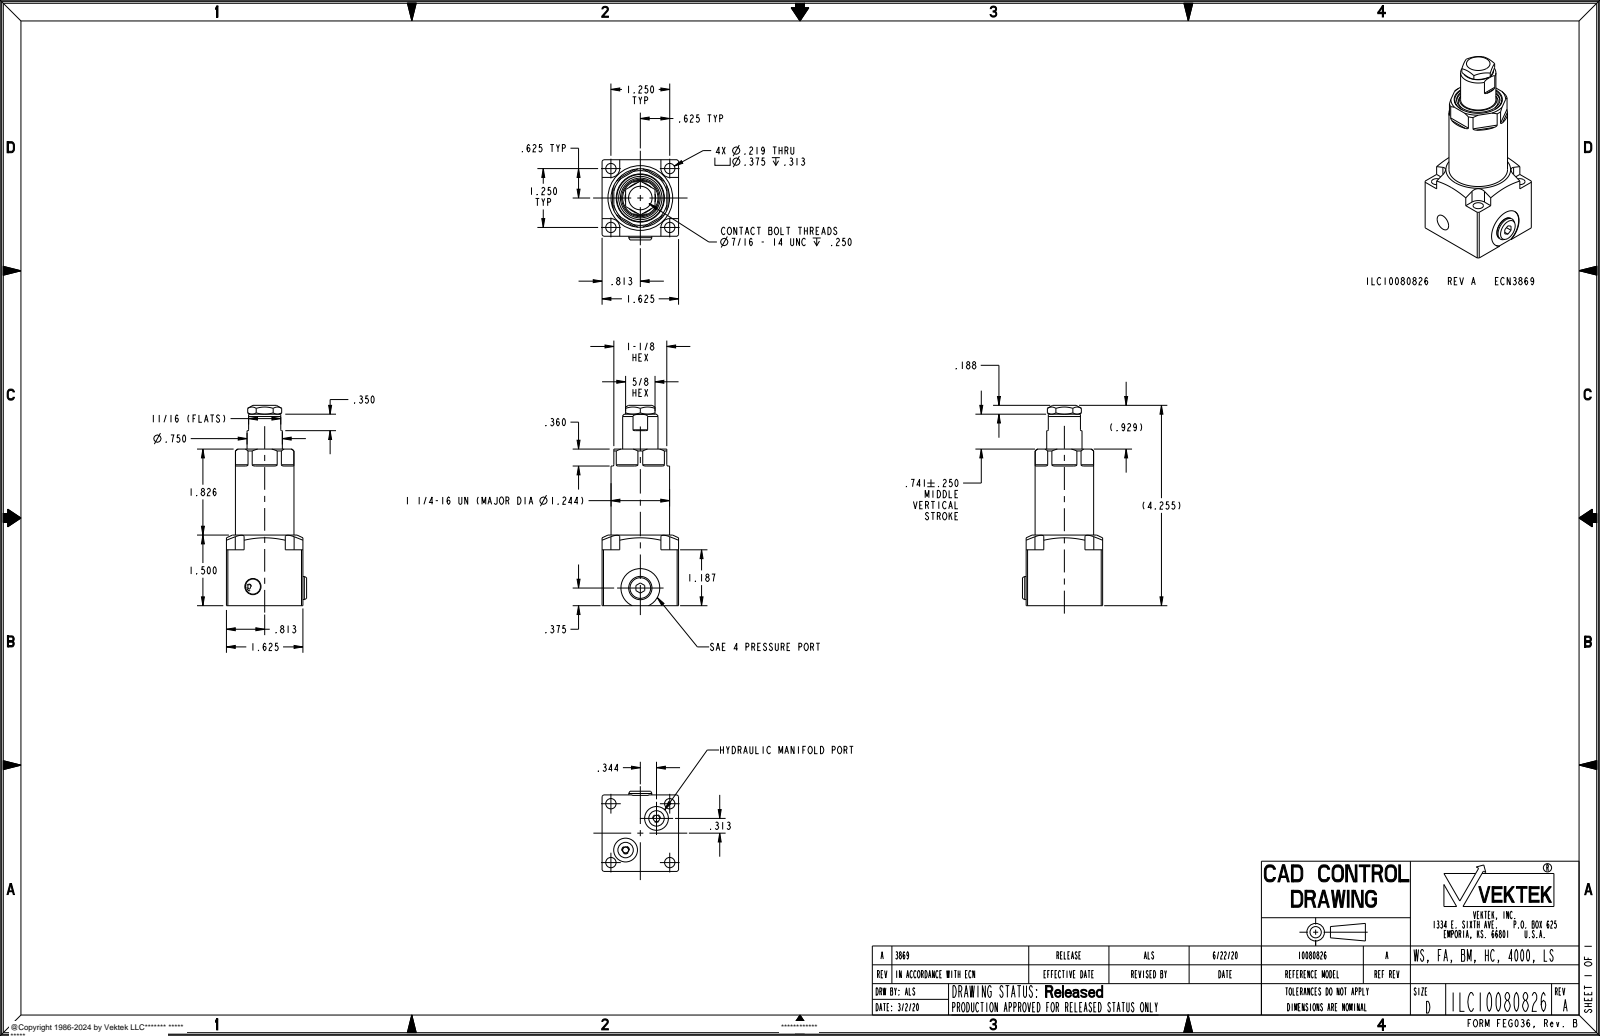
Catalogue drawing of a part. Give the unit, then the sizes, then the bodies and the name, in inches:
Units: inches
Overall size (bounding box): 4.255 × 1.704 × 1.625
Round holes (diameter × count): ⌀0.219 ×4, ⌀0.136 ×2, ⌀0.164 ×2, ⌀0.328 ×2, ⌀0.505 ×2, ⌀0.125 ×1, ⌀0.368 ×1, ⌀0.392 ×1, ⌀0.825 ×1, ⌀0.92 ×1
Round bosses / shafts (diameter × count): ⌀0.437 ×2, ⌀1.244 ×1, ⌀1 ×1, ⌀0.75 ×1, ⌀0.438 ×1
Partial cylindrical surfaces — rounded edges, fillets, slot ends (radius × count): R0.027 ×6, R0.187 ×4, R0.018 ×2
Main face-to-face distances: 1.625, 1.625, 0.25, 1.125, 1.187, 1.615, 1.375, 0.875, 1.5, 0.313
Hole centre spacings: 0.884, 1.25, 1.769, 0.41, 0.42, 0.465, 0.476, 0.94
Volume: 5.973 in³ · Surface area: 30.87 in²
Bodies: 1 solid, 171 faces (70 planar, 57 cylindrical, 44 other)
Part name (STEP PRODUCT): ILC10080826
STEP written by: PRO/ENGINEER BY PARAMETRIC TECHNOLOGY CORPORATION, 2013320 (CONFIG_CONTROL_DESIGN)
